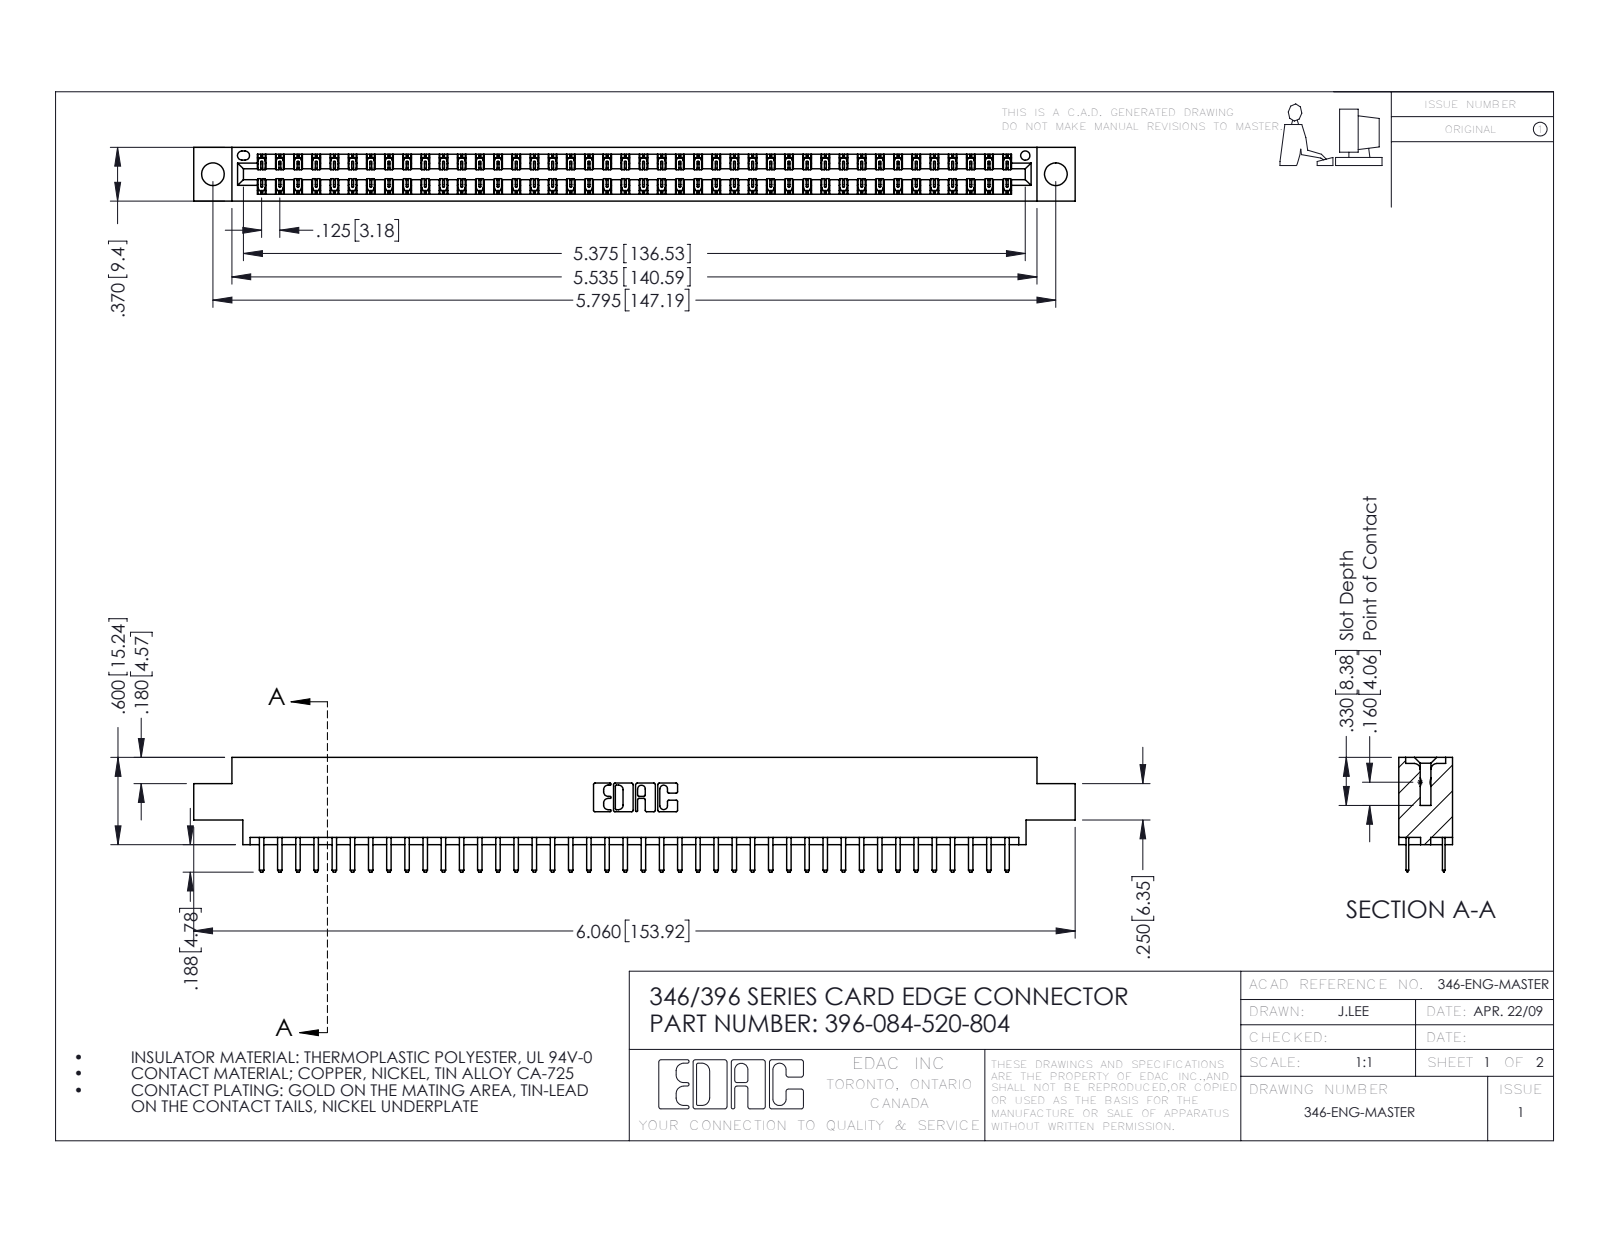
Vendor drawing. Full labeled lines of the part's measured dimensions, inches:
Part name (STEP PRODUCT): 346 Part_0.170 Offset - 0.156 Dia-TH; 396-084-520-804; 345-292-001_345-293-120
STEP written by: SolidWorks 2016 (CONFIG_CONTROL_DESIGN)
Units: inches
Bodies: 85 solids, 4830 faces (3188 planar, 1642 cylindrical, 0 other)
Overall size (bounding box): 6.06 × 0.788 × 0.37
Volume: 0.899 in³ · Surface area: 31.24 in²
Round holes (diameter × count): ⌀0.156 ×2, ⌀0.064 ×1
Partial cylindrical surfaces — rounded edges, fillets, slot ends (radius × count): R0.006 ×126, R0.01 ×88, R0.01 ×22, R0.007 ×6, R0.031 ×6, R0.026 ×3, R0.014 ×2, R0.022 ×2
Main face-to-face distances: 0.048, 0.322, 0.25, 0.37, 0.275, 0.072, 0.298, 0.025, 0.148, 0.222
Hole centre spacings: 0.246, 5.586, 5.795
